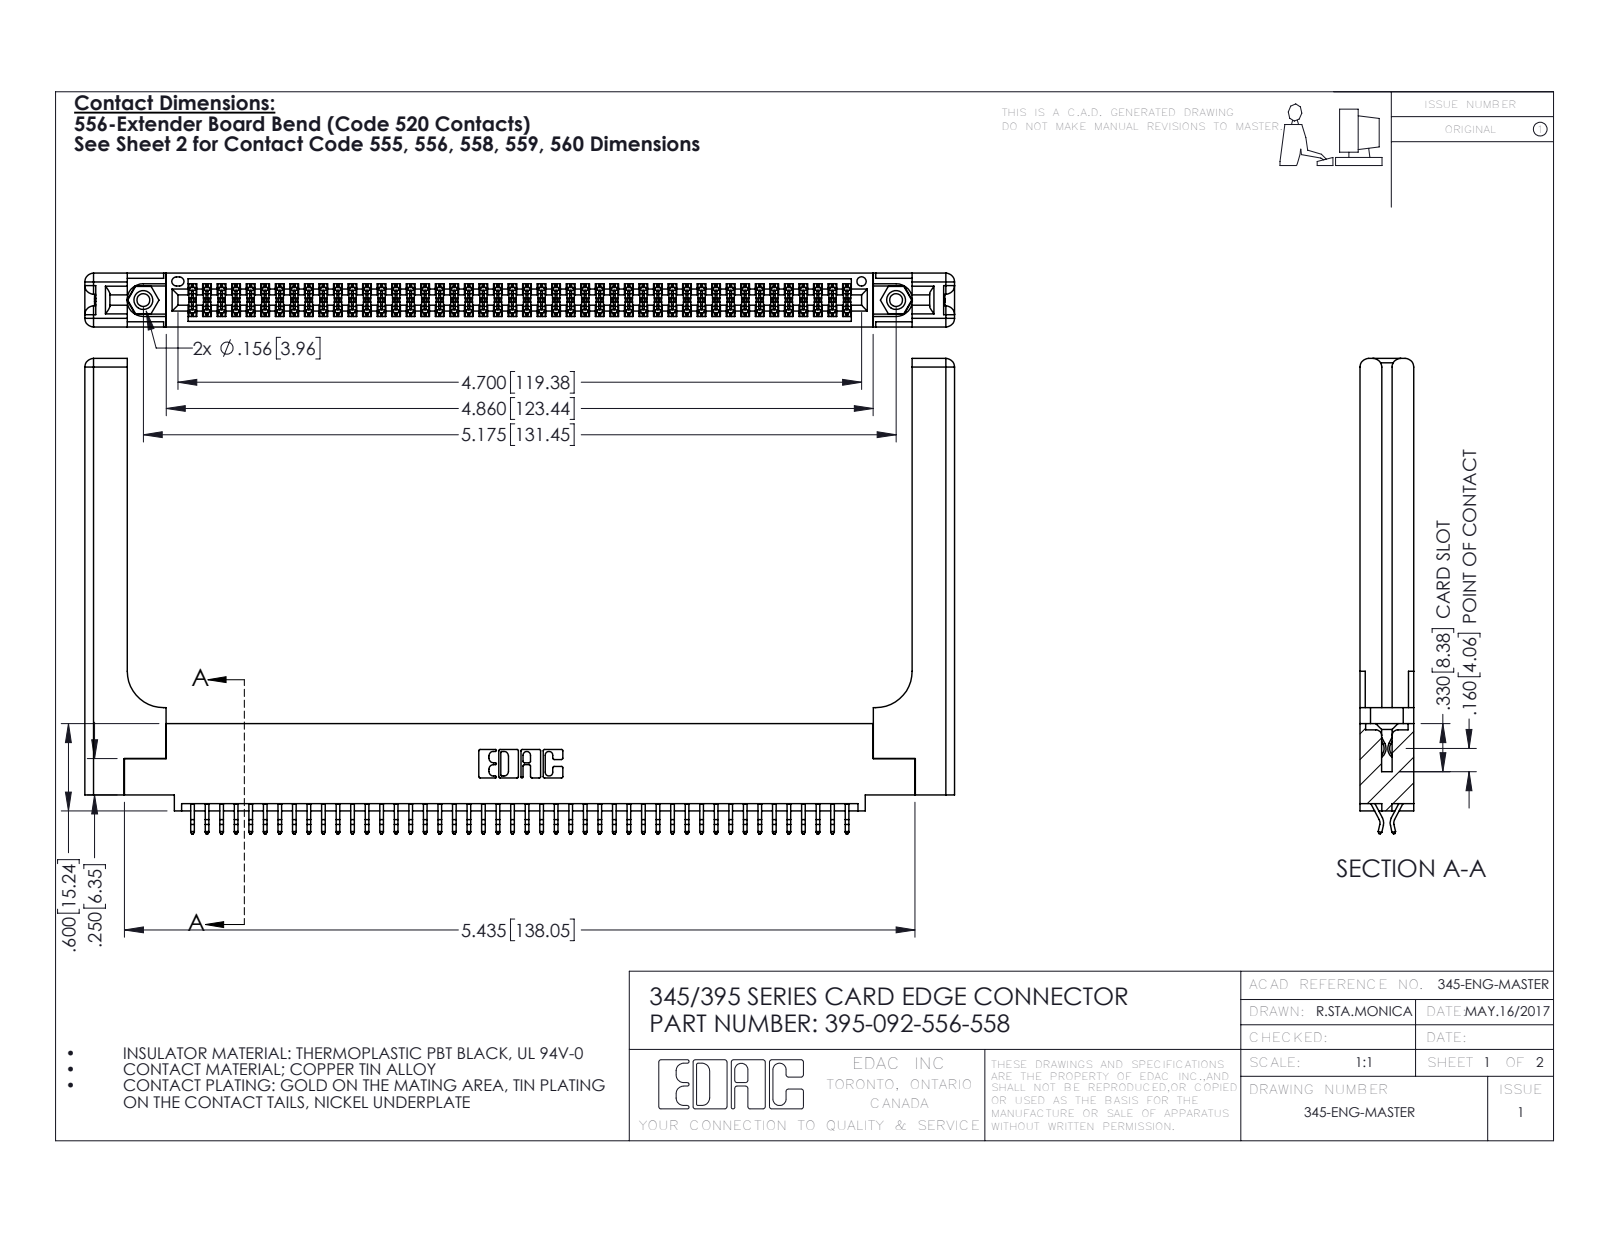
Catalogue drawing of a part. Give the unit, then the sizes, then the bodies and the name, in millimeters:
Units: millimetres
Overall size (bounding box): 151.9 × 83 × 9.4
Round holes (diameter × count): ⌀2.3 ×2, ⌀3.2 ×2, ⌀4 ×2, ⌀1.6 ×1
Round bosses / shafts (diameter × count): ⌀3.9 ×2
Partial cylindrical surfaces — rounded edges, fillets, slot ends (radius × count): R0.2 ×138, R0.3 ×22, R1.5 ×16, R0.2 ×6, R0.8 ×6, R0.7 ×3, R0.3 ×2, R0.4 ×2
Main face-to-face distances: 1.8, 9.4, 7.6, 0.6, 5.1, 2.5, 6.9, 5.7, 3.8, 3.8
Hole centre spacings: 6.9, 125.5, 131.4
Volume: 23 190 mm³ · Surface area: 26 900 mm²
Bodies: 97 solids, 5538 faces (3636 planar, 1842 cylindrical, 60 other)
Part name (STEP PRODUCT): 345-250-001_345-250-001-102; 345-292-001_556 Tail; 345-220-058_345-220-058; 395-092-556-558 (+1 more)
STEP written by: SolidWorks 2016 (CONFIG_CONTROL_DESIGN)
